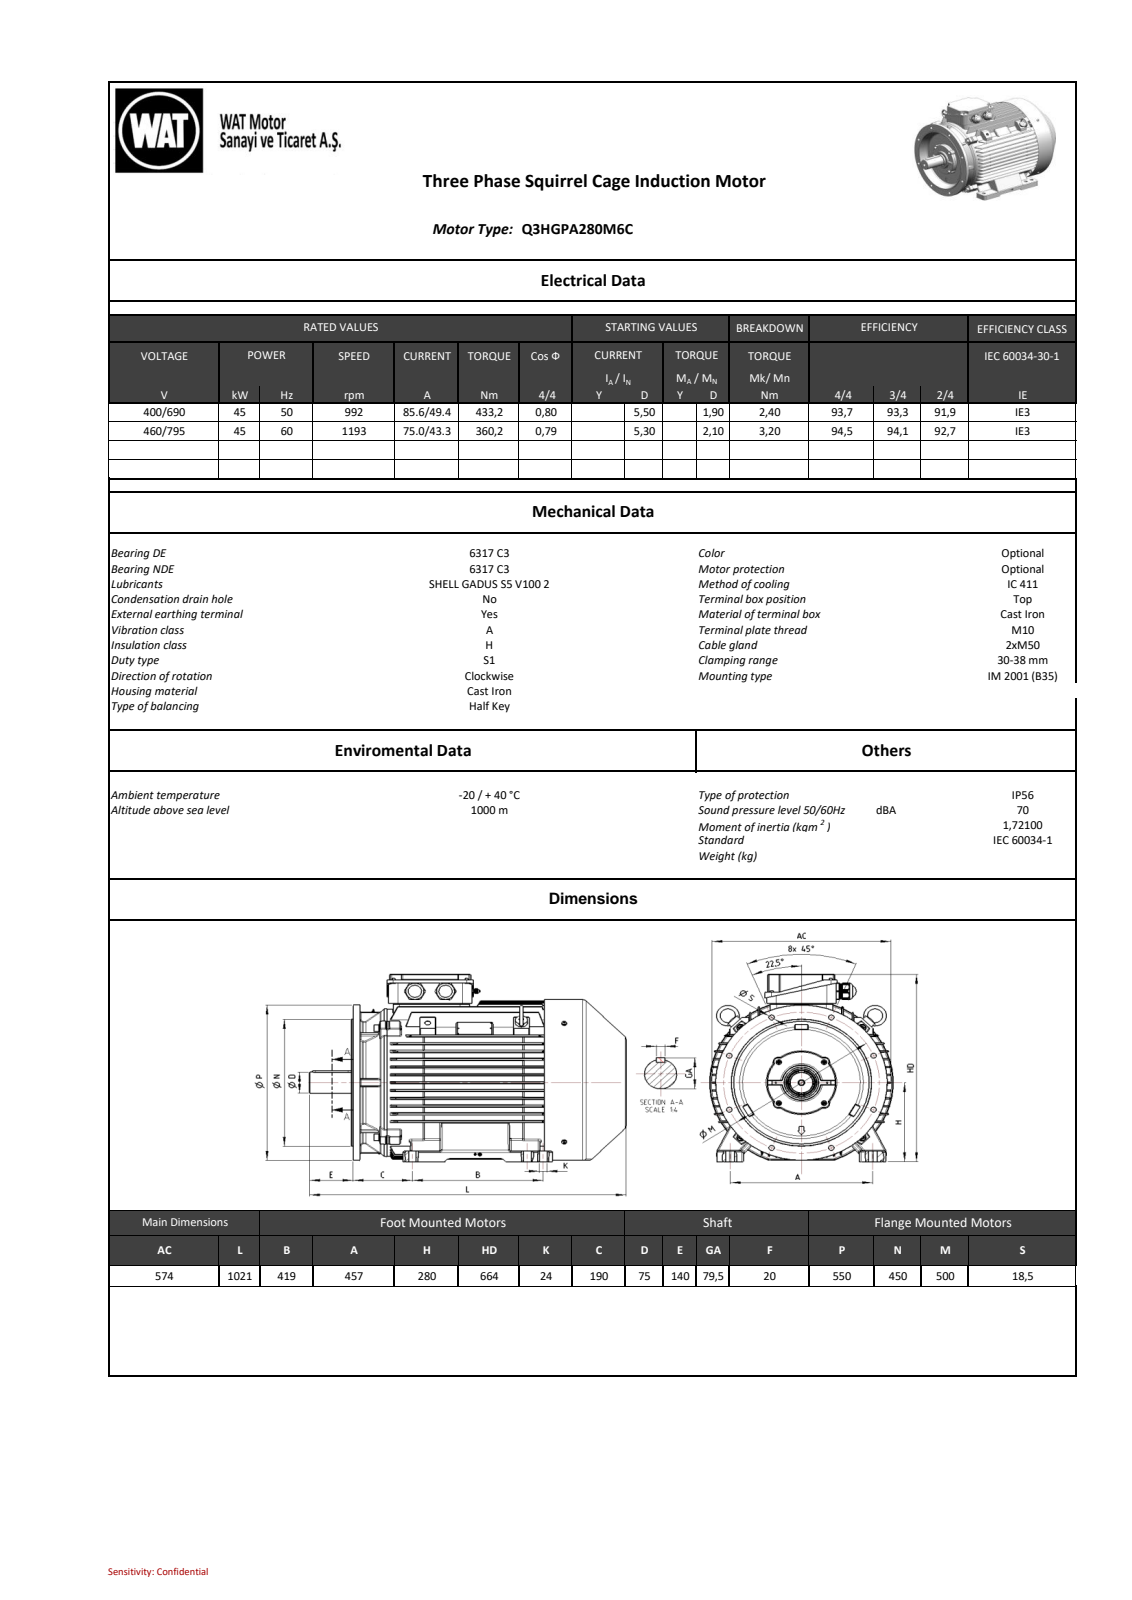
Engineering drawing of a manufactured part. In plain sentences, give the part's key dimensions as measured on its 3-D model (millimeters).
The part is named "AB_objects". Its 3-D file was written by "SIEMENS PLM Software NX2206.8101 (AUTOMOTIVE_DESIGN)". It is 0 solids with 4224 faces: 1657 planar, 1137 cylindrical and 1430 other. Overall it measures 1020.89 by 664.21 by 588 millimeters. Round holes: 10 of diameter 18.5, 4 of diameter 14.75, 1 of diameter 4.5, 1 of diameter 7.2, 1 of diameter 10, 1 of diameter 18, 1 of diameter 21, 1 of diameter 585. Round bosses or shafts: 4 of diameter 27.4, 4 of diameter 23.67, 4 of diameter 16, 4 of diameter 15.73, 4 of diameter 10, 3 of diameter 18.1, 2 of diameter 58, 2 of diameter 55.1. Partial cylindrical surfaces (rounded edges, fillets, slot ends): 291 of radius 1.5, 82 of radius 3, 71 of radius 2, 58 of radius 1, 42 of radius 5, 24 of radius 4, 18 of radius 0.2, 16 of radius 8. The main face-to-face distances are 27.62, 55.24, 55.79, 31.52, 221.79, 23, 30, 53, 13.5, 27.9. The hole center spacings are 104.7, 191.34, 250, 291.49, 353.55, 435.47, 461.94, 513.46.
